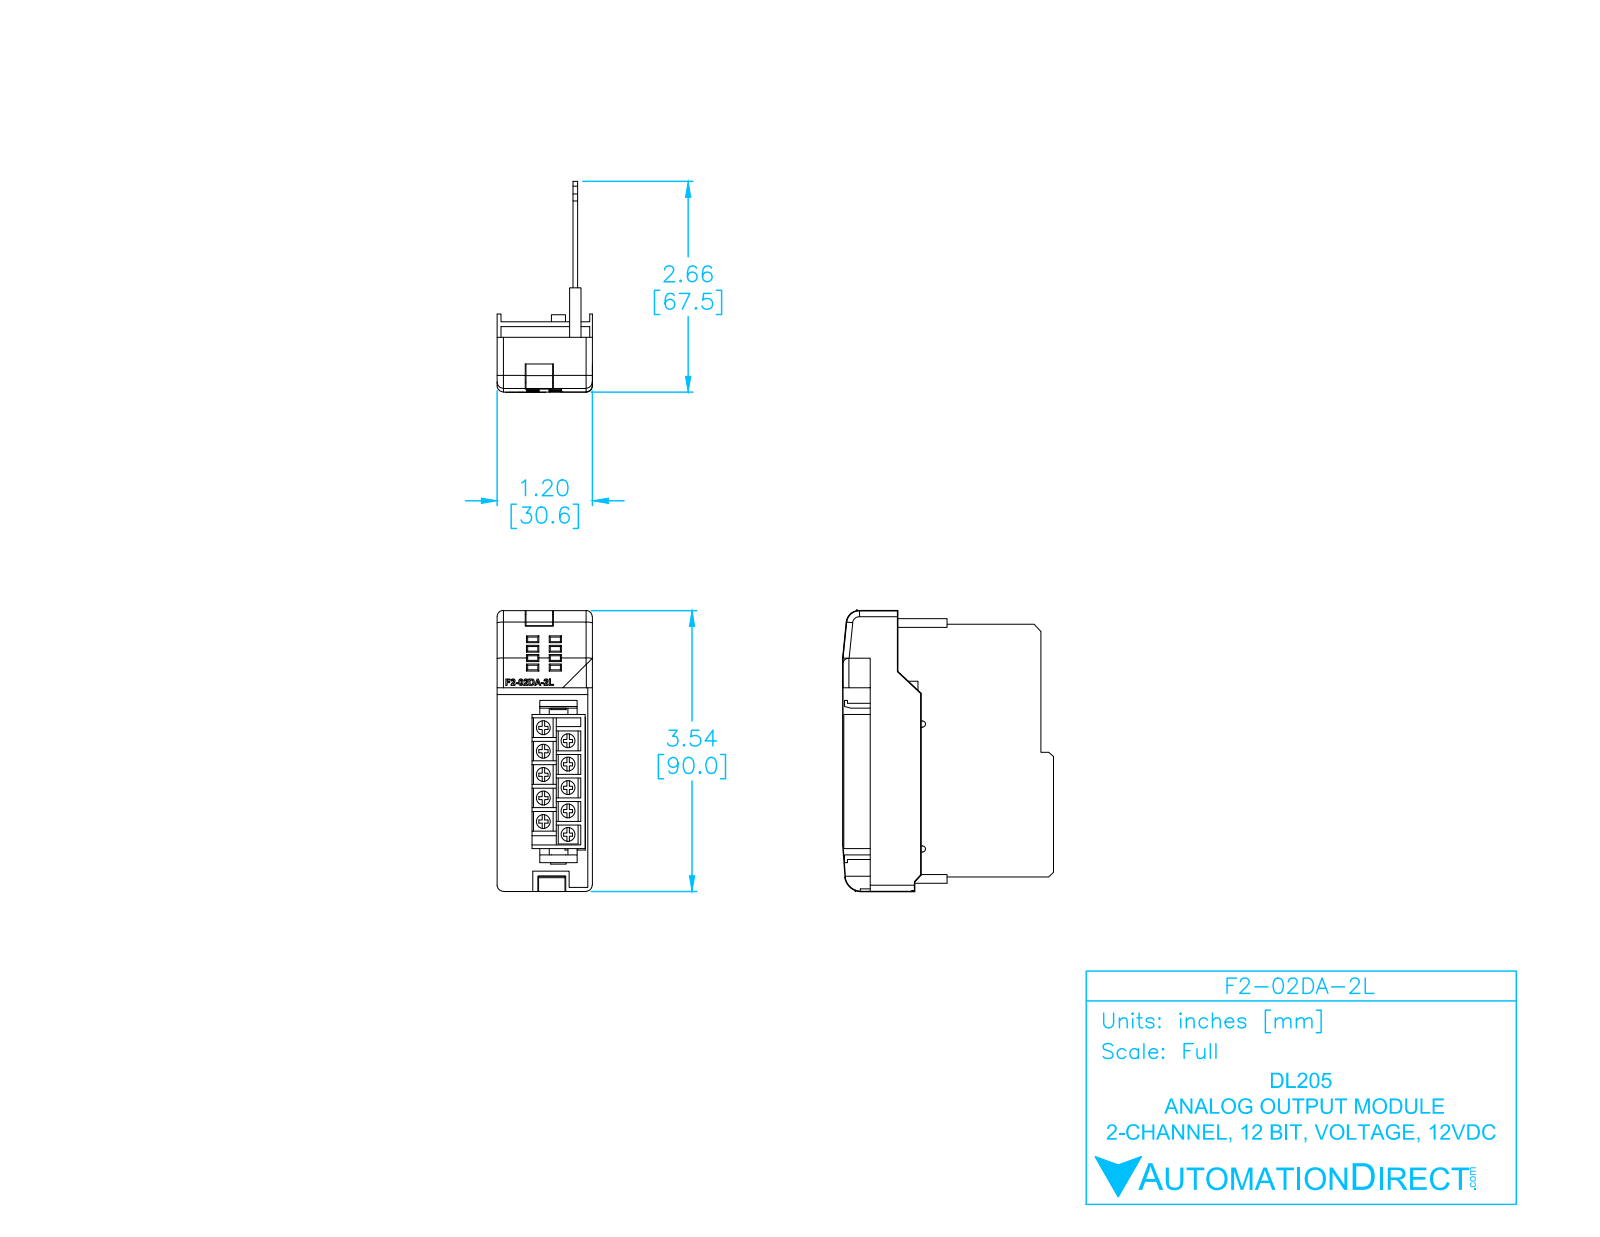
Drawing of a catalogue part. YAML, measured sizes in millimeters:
part_name: "F2-02DA-2L_ModuleCase_light_NEW"
step_written_by: "SolidWorks 2009 (AUTOMOTIVE_DESIGN)"
units: millimeters
bodies: {solids: 6, faces: 587, planar: 420, cylindrical: 75, other: 92}
overall_size: [90, 67.56, 30.55]
volume: 25374
surface_area: 28533
round_bosses_or_shafts:
  - {diameter: 4.5, count: 10}
partial_cylinders:
  - {radius: 0.35, count: 16}
  - {radius: 2, count: 9}
  - {radius: 0.25, count: 2}
  - {radius: 1, count: 2}
  - {radius: 1.25, count: 2}
  - {radius: 4.12, count: 1}
  - {radius: 5.39, count: 1}
face_to_face_distances: [1.5, 4.72, 6.22, 2.37, 3.87, 2.35, 3.22, 0.85, 8.14, 24.28]
